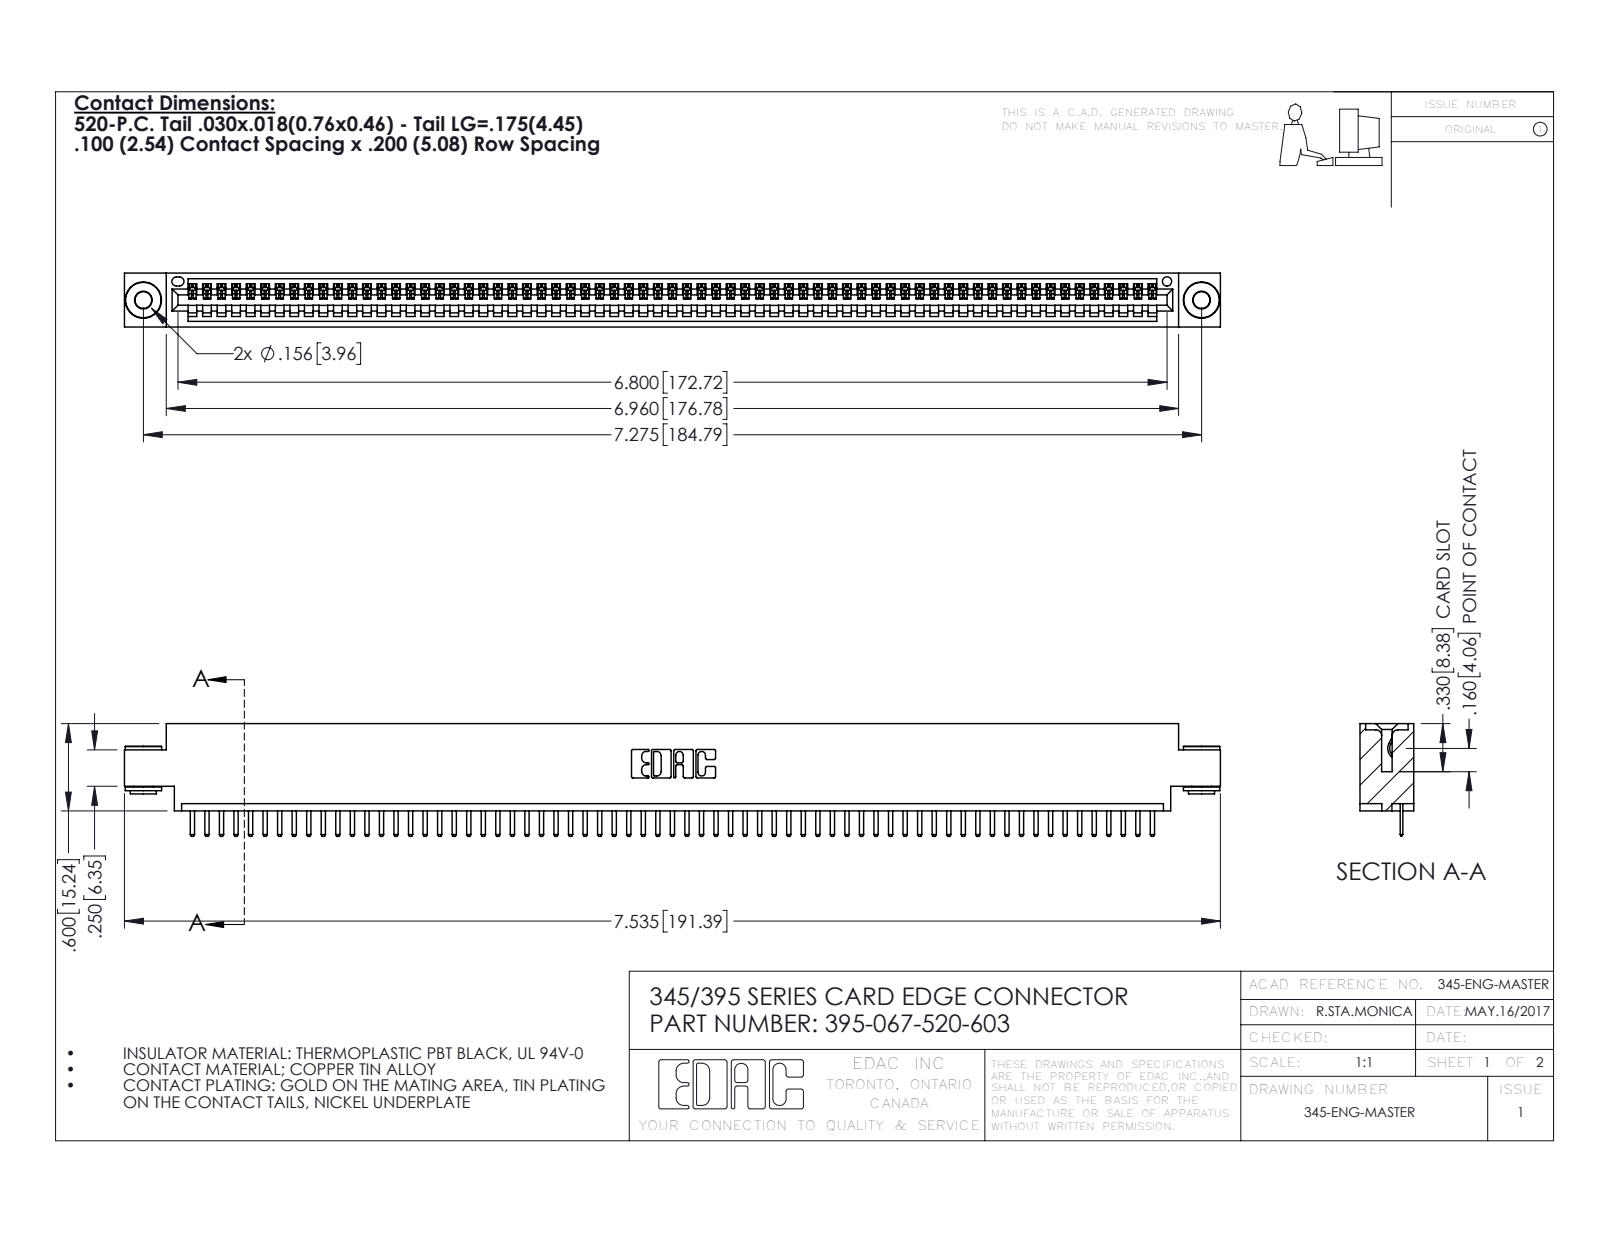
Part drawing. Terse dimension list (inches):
name: 345-292-001_345-293-120; 345-250-002_345-250-002-102; 395-067-520-603; 345 Part_0.170 Offset - 0.156 Dia-TH
written by: SolidWorks 2016 (CONFIG_CONTROL_DESIGN)
unit: in
bodies: 70 solids, 4322 faces (2908 planar, 1406 cylindrical, 8 other)
size: 7.535 × 0.775 × 0.37
volume: 1.104 in³; area: 37.35 in²
holes: 2× ⌀0.116, 2× ⌀0.156, 1× ⌀0.064
bosses: 2× ⌀0.25, 2× ⌀0.18, 2× ⌀0.136
rounds: 136× R0.01, 134× R0.006, 22× R0.01, 6× R0.007, 6× R0.031, 3× R0.026, 2× R0.031, 2× R0.04
face distances: 0.072, 0.298, 0.37, 0.2, 0.098, 0.272, 0.025, 0.225, 0.072, 0.175
hole spacings: 0.27, 7.039, 7.275
